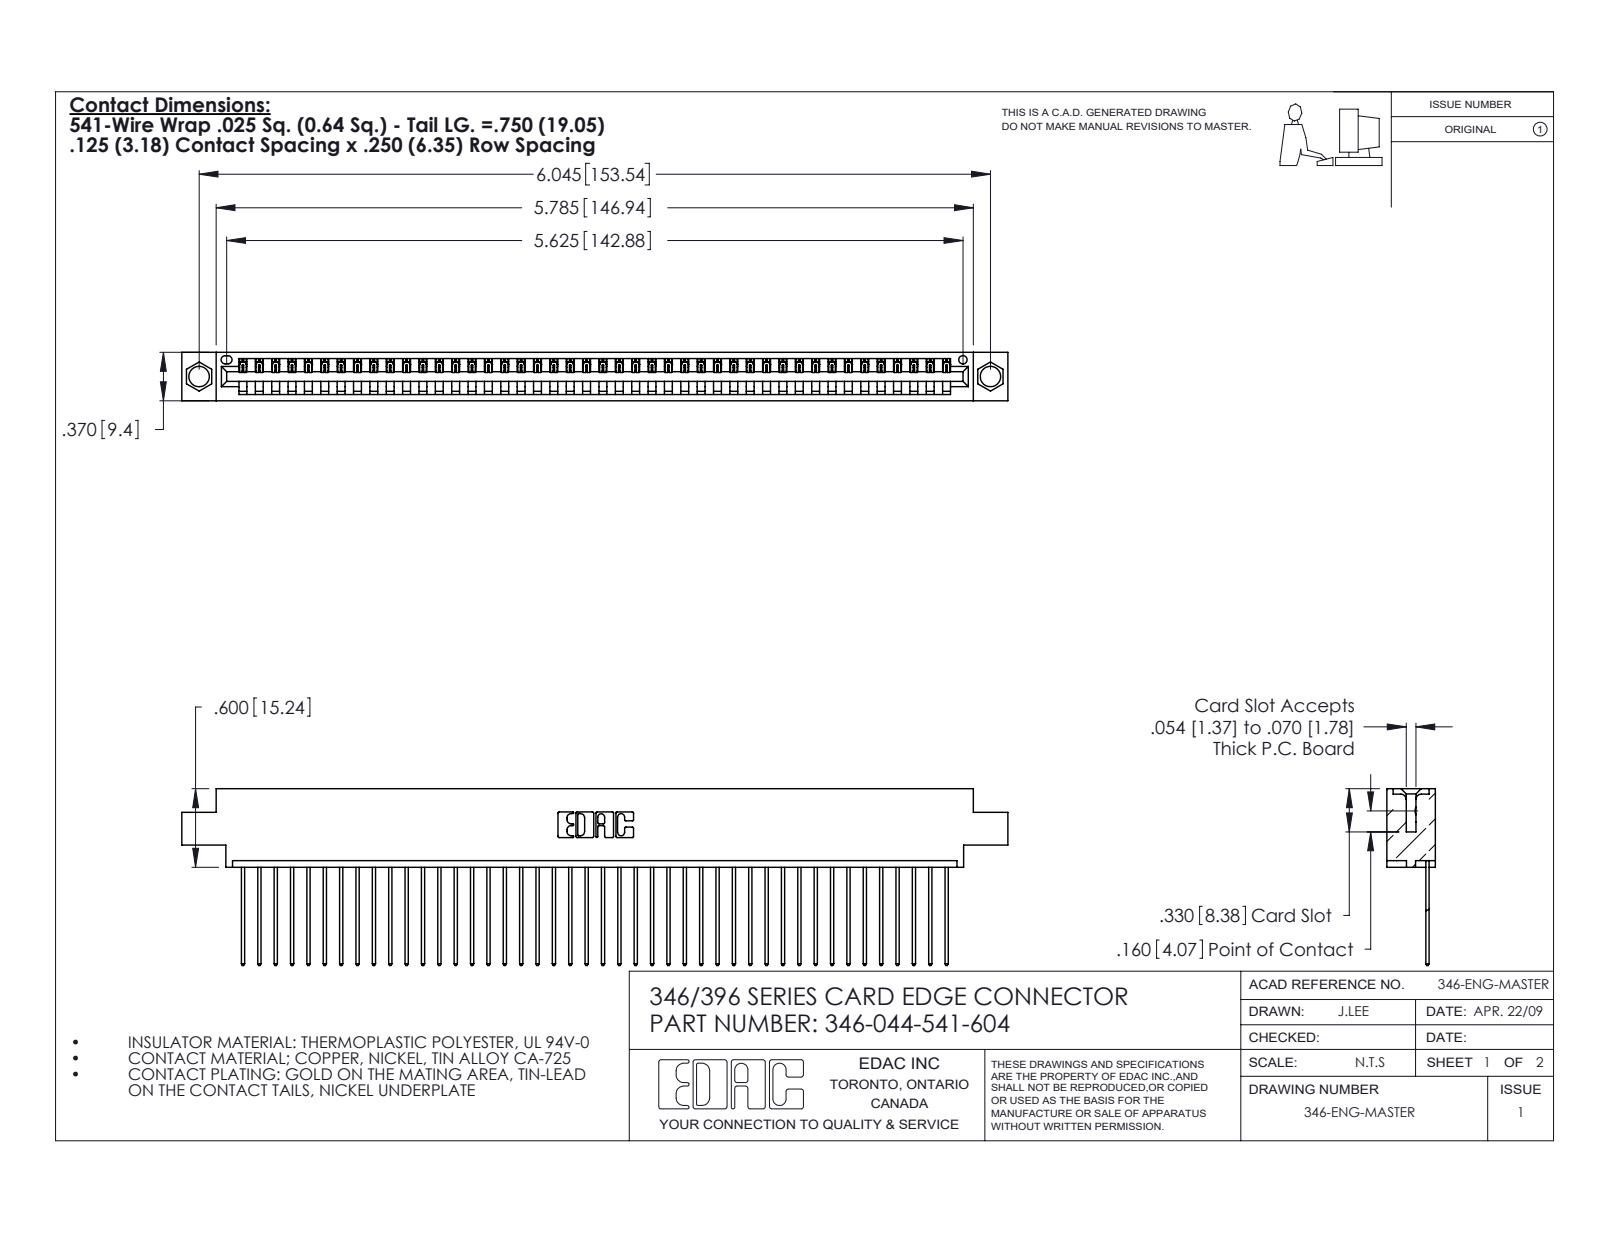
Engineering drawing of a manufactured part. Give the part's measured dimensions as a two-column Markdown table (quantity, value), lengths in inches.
| quantity | value |
| --- | --- |
| part name | 346 Part_0.170 Offset - 0.156 Dia-TH; 345-292-001_345-293-141; 346-044-541-604 |
| STEP written by | SolidWorks 2020 (CONFIG_CONTROL_DESIGN) |
| units | inches |
| bodies | 45 solids, 2692 faces (1854 planar, 838 cylindrical, 0 other) |
| overall size | 6.31 × 1.35 × 0.37 |
| volume | 0.93 in³ |
| surface area | 30.9 in² |
| round holes (diameter × count) | 0.156 × 2, 0.064 × 1 |
| partial cylindrical surfaces (radius × count) | 0.006 × 88, 0.01 × 88, 0.01 × 22, 0.007 × 6, 0.031 × 6, 0.026 × 3, 0.031 × 2, 0.04 × 2 |
| main face-to-face distances | 0.048, 0.322, 0.37, 0.25, 0.072, 0.298, 0.025, 0.222, 0.148, 0.1 |
| hole center spacings | 0.246, 5.836, 6.045 |
